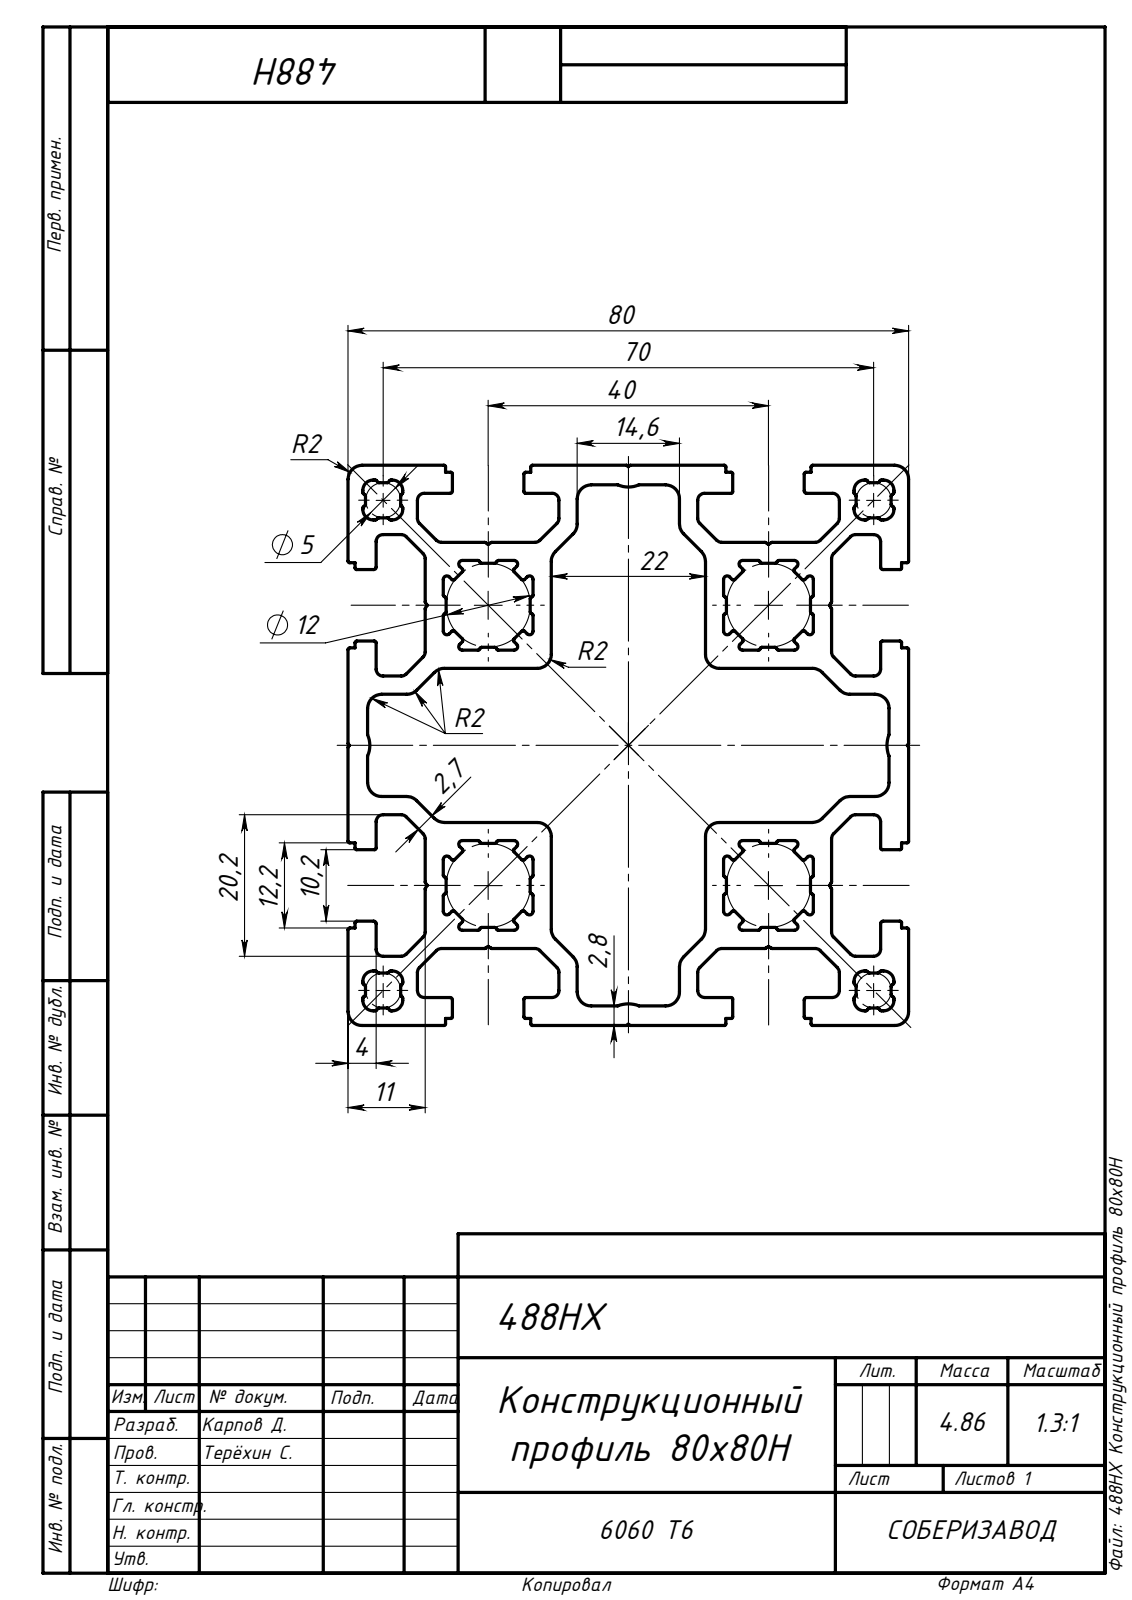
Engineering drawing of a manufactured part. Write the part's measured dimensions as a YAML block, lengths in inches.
step_written_by: "SolidWorks 2019 (AUTOMOTIVE_DESIGN)"
units: inches
bodies: {solids: 1, faces: 726, planar: 362, cylindrical: 364, other: 0}
overall_size: [39.374, 3.15, 3.15]
volume: 109.8
surface_area: 1843
partial_cylinders:
  - {radius: 0.01, count: 216}
  - {radius: 0.039, count: 48}
  - {radius: 0.02, count: 32}
  - {radius: 0.079, count: 32}
  - {radius: 0.059, count: 16}
  - {radius: 0.014, count: 8}
  - {radius: 0.157, count: 4}
face_to_face_distances: [1.575, 1.142, 2.008, 3.15, 0.433, 2.717, 0.709, 0.102, 1.113, 0.606]
